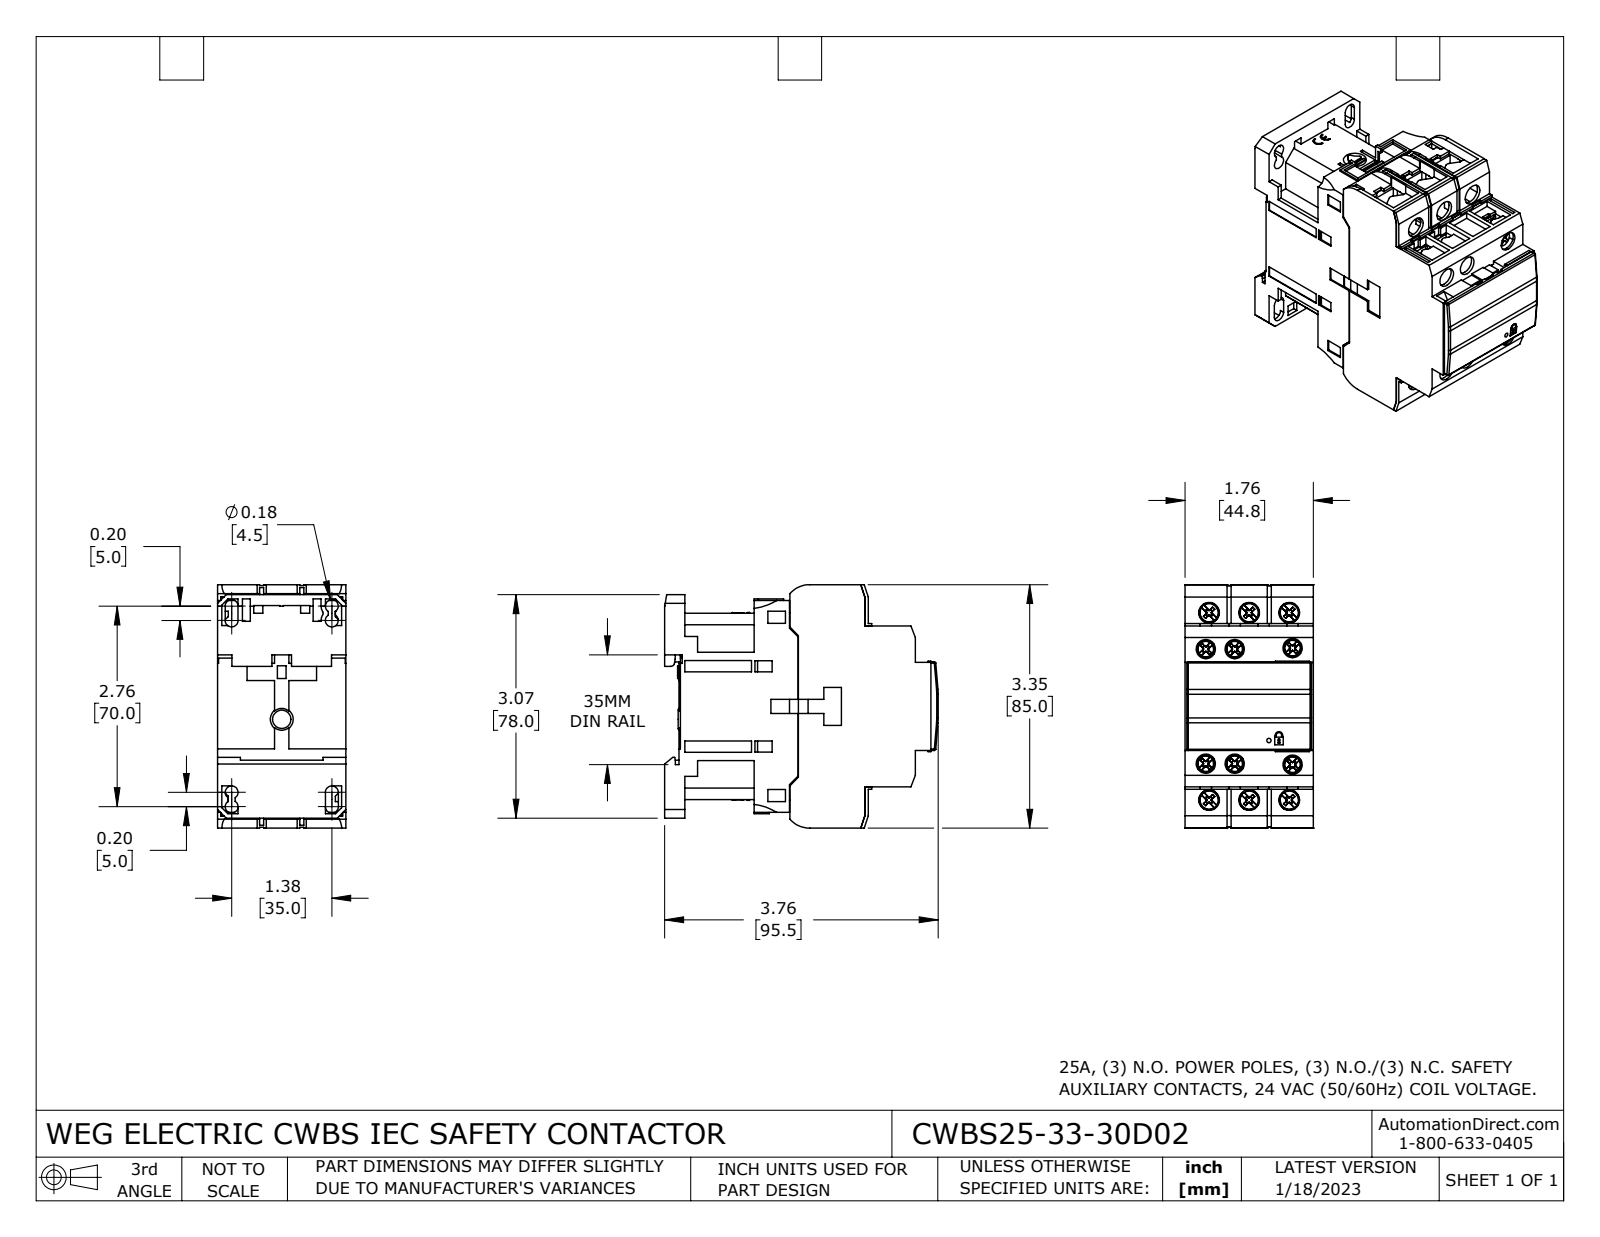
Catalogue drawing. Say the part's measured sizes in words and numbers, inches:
The part is named "CWBS25-33-30D02". Its 3-D file was written by "SolidWorks 2021 (CONFIG_CONTROL_DESIGN)". It is 42 solids with 2461 faces: 1808 planar, 446 cylindrical and 207 other. Overall it measures 3.76 by 3.346 by 1.764 inches. Its volume is 14.49 cubic inches and its surface area 108.8 square inches. Round holes: 6 of diameter 0.124, 6 of diameter 0.142, 6 of diameter 0.264, 6 of diameter 0.283, 4 of diameter 0.177, 1 of diameter 0.059. Round bosses or shafts: 6 of diameter 0.201, 6 of diameter 0.169, 6 of diameter 0.157, 6 of diameter 0.138, 4 of diameter 0.107, 2 of diameter 0.107. Partial cylindrical surfaces (rounded edges, fillets, slot ends): 42 of radius 0.02, 24 of radius 0.028, 12 of radius 0.071, 12 of radius 0.081, 12 of radius 0.964, 12 of radius 1.079, 12 of radius 2.128, 12 of radius 3.127. The main face-to-face distances are 1.764, 0.047, 1.691, 0.132, 1.823, 0.024, 0.217, 3.445, 0.276, 1.717. The hole center spacings are 0.551, 2.633, 2.575, 0.165, 0.174, 0.197, 0.398, 0.488.
